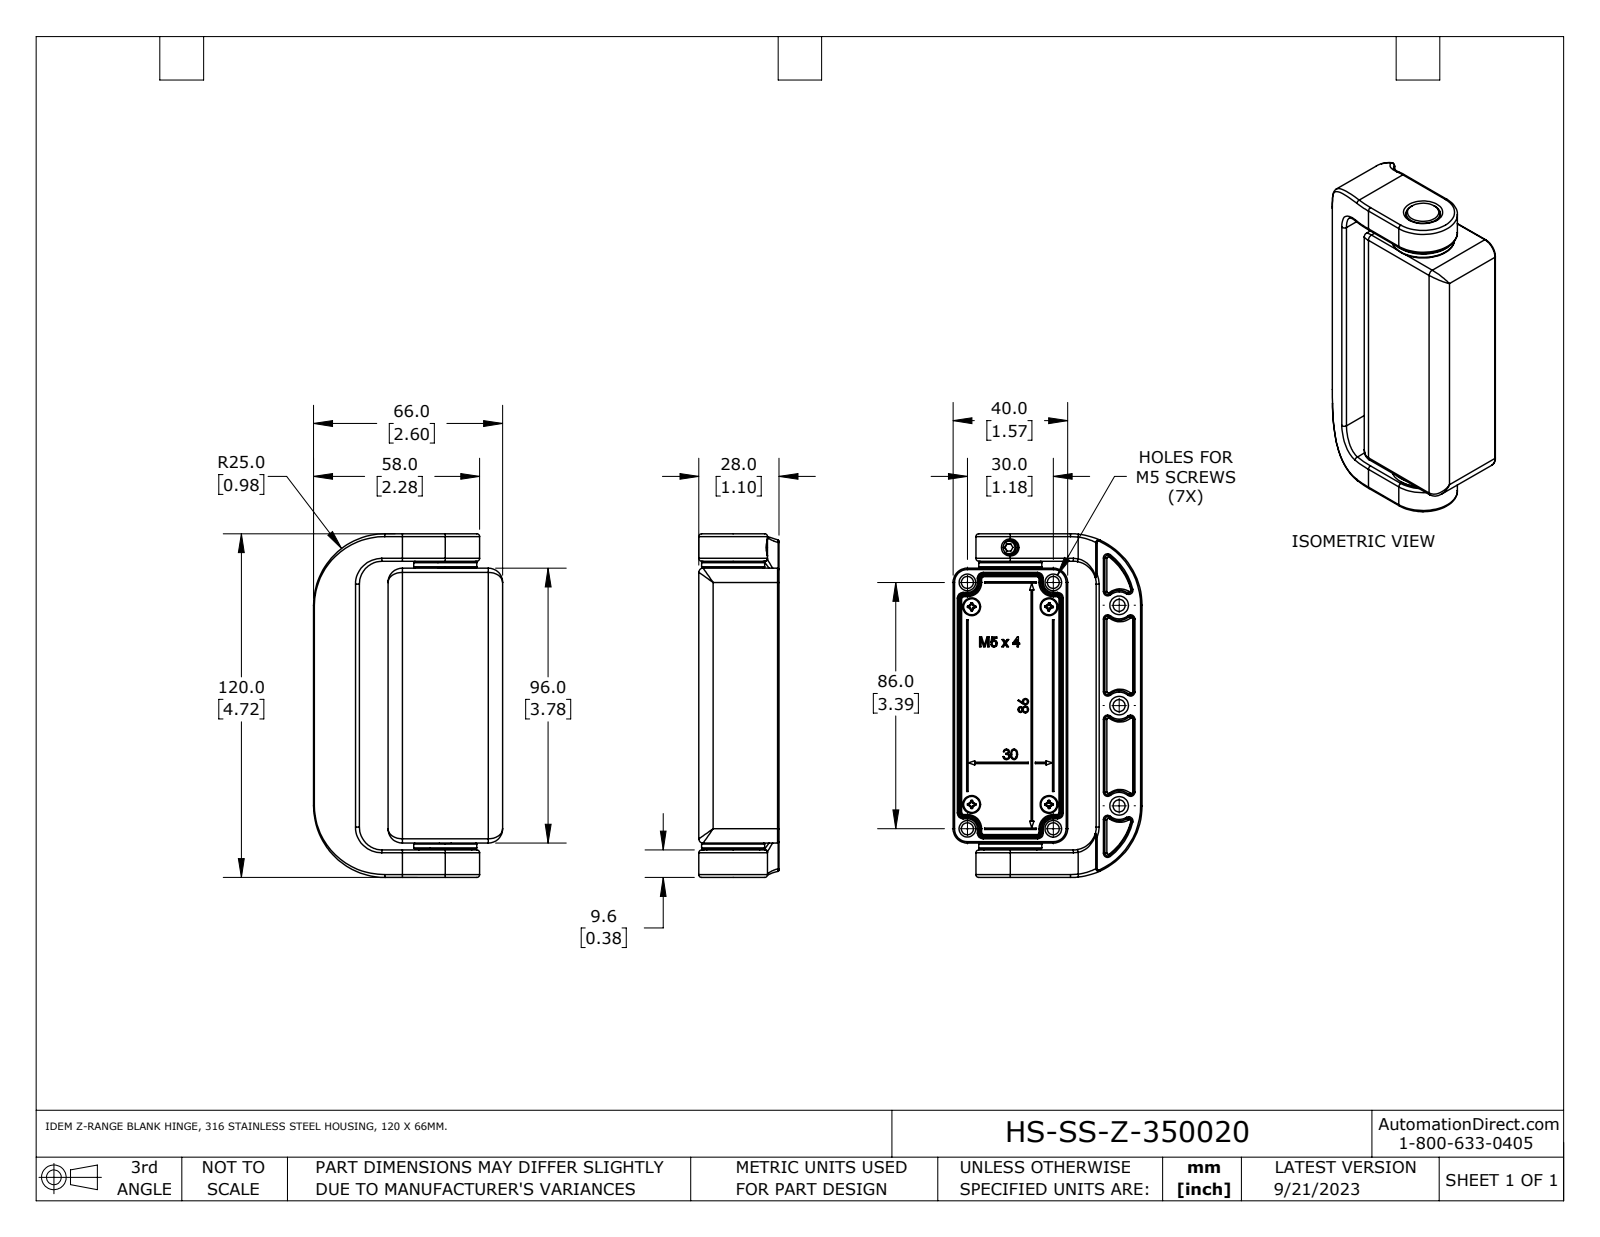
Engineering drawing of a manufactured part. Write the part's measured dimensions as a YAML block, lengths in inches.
part_name: "HS-SS-Z-350020"
step_written_by: "SolidWorks 2021 (AUTOMOTIVE_DESIGN)"
units: inches
bodies: {solids: 12, faces: 1130, planar: 274, cylindrical: 357, other: 499}
overall_size: [4.724, 2.598, 1.102]
volume: 5.704
surface_area: 82.2
round_holes:
  - {diameter: 0.165, count: 8}
  - {diameter: 0.098, count: 7}
  - {diameter: 0.118, count: 4}
  - {diameter: 0.138, count: 4}
  - {diameter: 0.079, count: 1}
  - {diameter: 0.13, count: 1}
  - {diameter: 0.197, count: 1}
  - {diameter: 0.315, count: 1}
  - {diameter: 0.323, count: 1}
  - {diameter: 0.472, count: 1}
  - {diameter: 0.476, count: 1}
  - {diameter: 0.594, count: 1}
round_bosses_or_shafts:
  - {diameter: 0.118, count: 4}
  - {diameter: 0.866, count: 1}
  - {diameter: 0.717, count: 1}
  - {diameter: 0.626, count: 1}
  - {diameter: 0.591, count: 1}
  - {diameter: 0.47, count: 1}
  - {diameter: 0.311, count: 1}
  - {diameter: 0.236, count: 1}
partial_cylinders:
  - {radius: 0.02, count: 90}
  - {radius: 0.039, count: 55}
  - {radius: 0.059, count: 10}
  - {radius: 0.008, count: 7}
  - {radius: 0.197, count: 6}
  - {radius: 0.118, count: 4}
  - {radius: 0.157, count: 4}
  - {radius: 0.177, count: 4}
face_to_face_distances: [0.984, 0.098, 0.157, 0.512, 0.118, 0.394, 1.083, 1.417, 0.886, 1.575]
hole_center_spacings: [0.323, 0.34, 0.457, 1.171, 3.052, 3.251, 1.063, 0.301]
